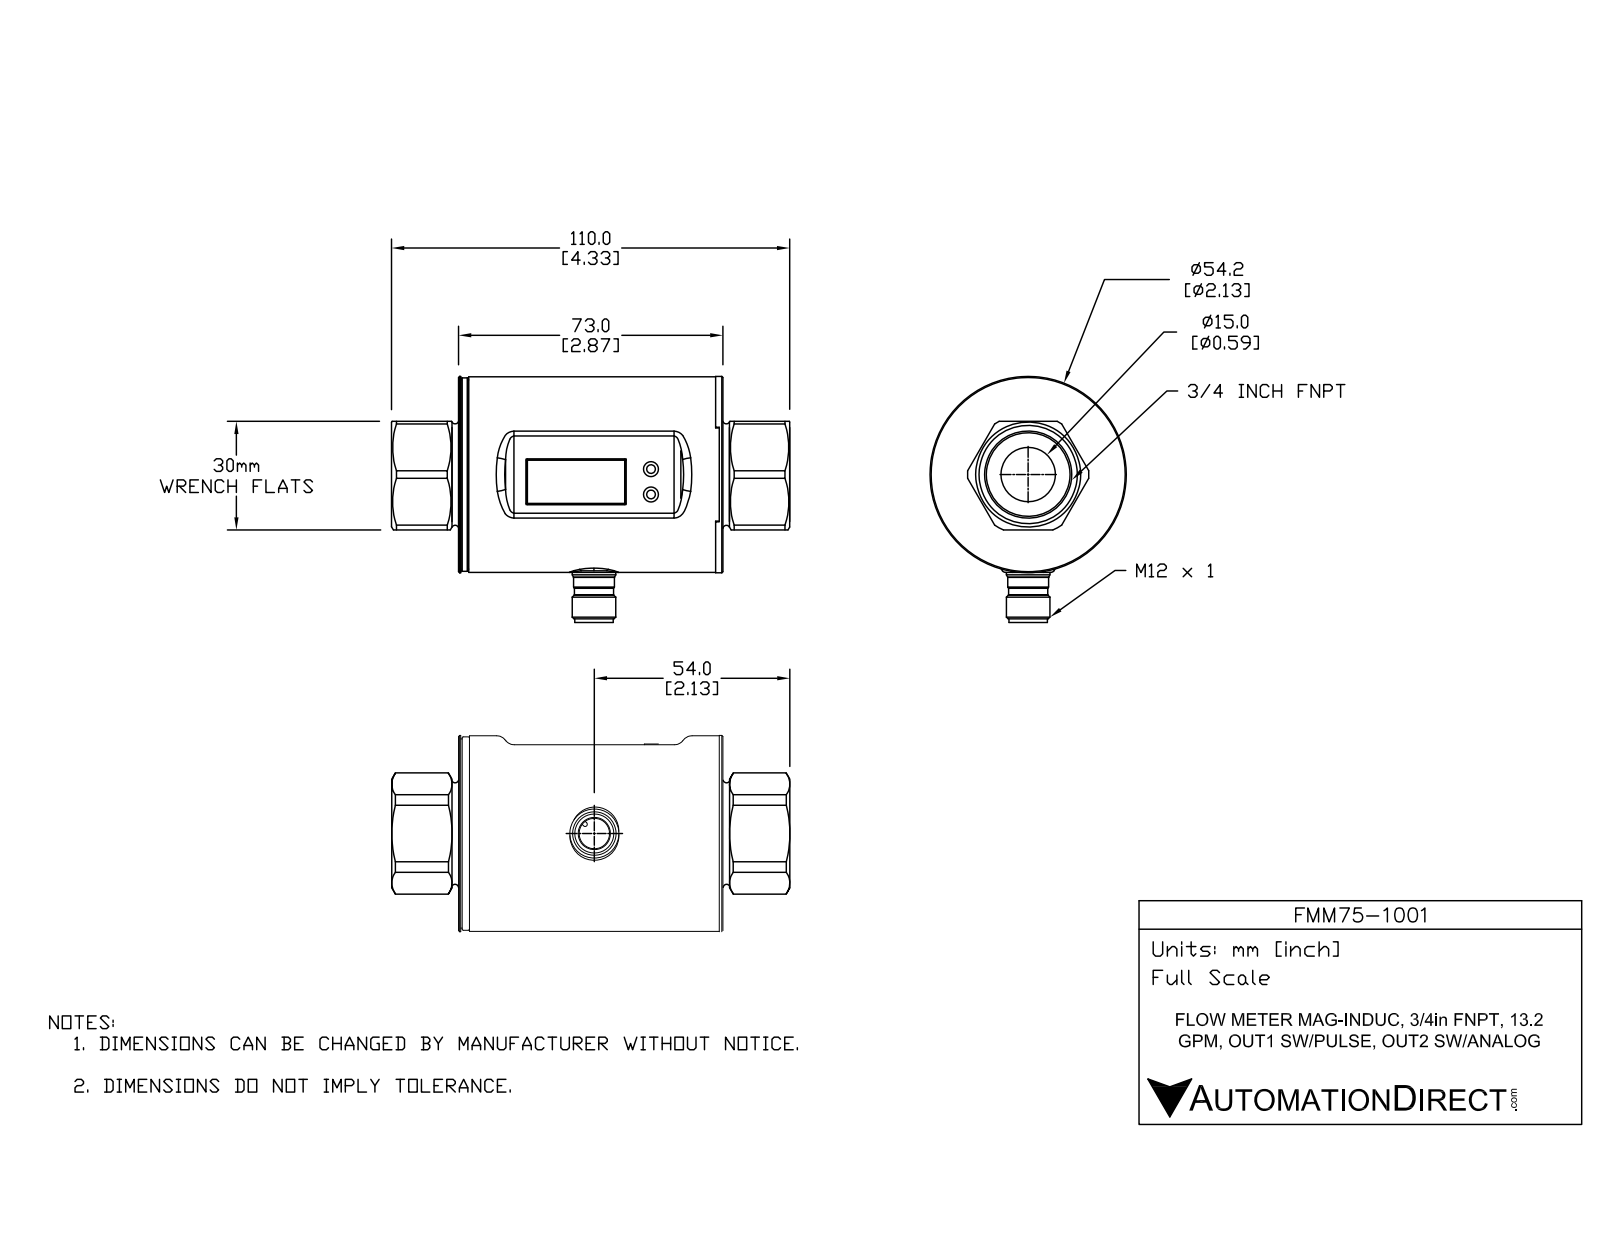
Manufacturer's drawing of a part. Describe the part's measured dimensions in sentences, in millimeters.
The part is named "FMM75-1001". Its 3-D file was written by "SolidWorks 2015 (AUTOMOTIVE_DESIGN)". It is 9 solids with 204 faces: 82 planar, 81 cylindrical and 41 other. Overall it measures 109.99 by 67.85 by 54.2 millimeters. Its volume is 47 414 cubic millimeters and its surface area 55 956 square millimeters. Round holes: 2 of diameter 1.5, 2 of diameter 3.6, 2 of diameter 4.11, 1 of diameter 8.4, 1 of diameter 12, 1 of diameter 15, 1 of diameter 23.1, 1 of diameter 52. Round bosses or shafts: 2 of diameter 3.9, 1 of diameter 54.2, 1 of diameter 54, 1 of diameter 53.4, 1 of diameter 52.2, 1 of diameter 12, 1 of diameter 11.3, 1 of diameter 10.6. Partial cylindrical surfaces (rounded edges, fillets, slot ends): 4 of radius 1, 2 of radius 0.3, 2 of radius 2, 2 of radius 3, 1 of radius 0.6, 1 of radius 16.75. The main face-to-face distances are 70, 2, 5, 68, 71.7, 1, 72, 72.7, 73, 3. The hole center spacings are 13, 1.25, 7, 8, 9.25, 21, 22.25, 26.
